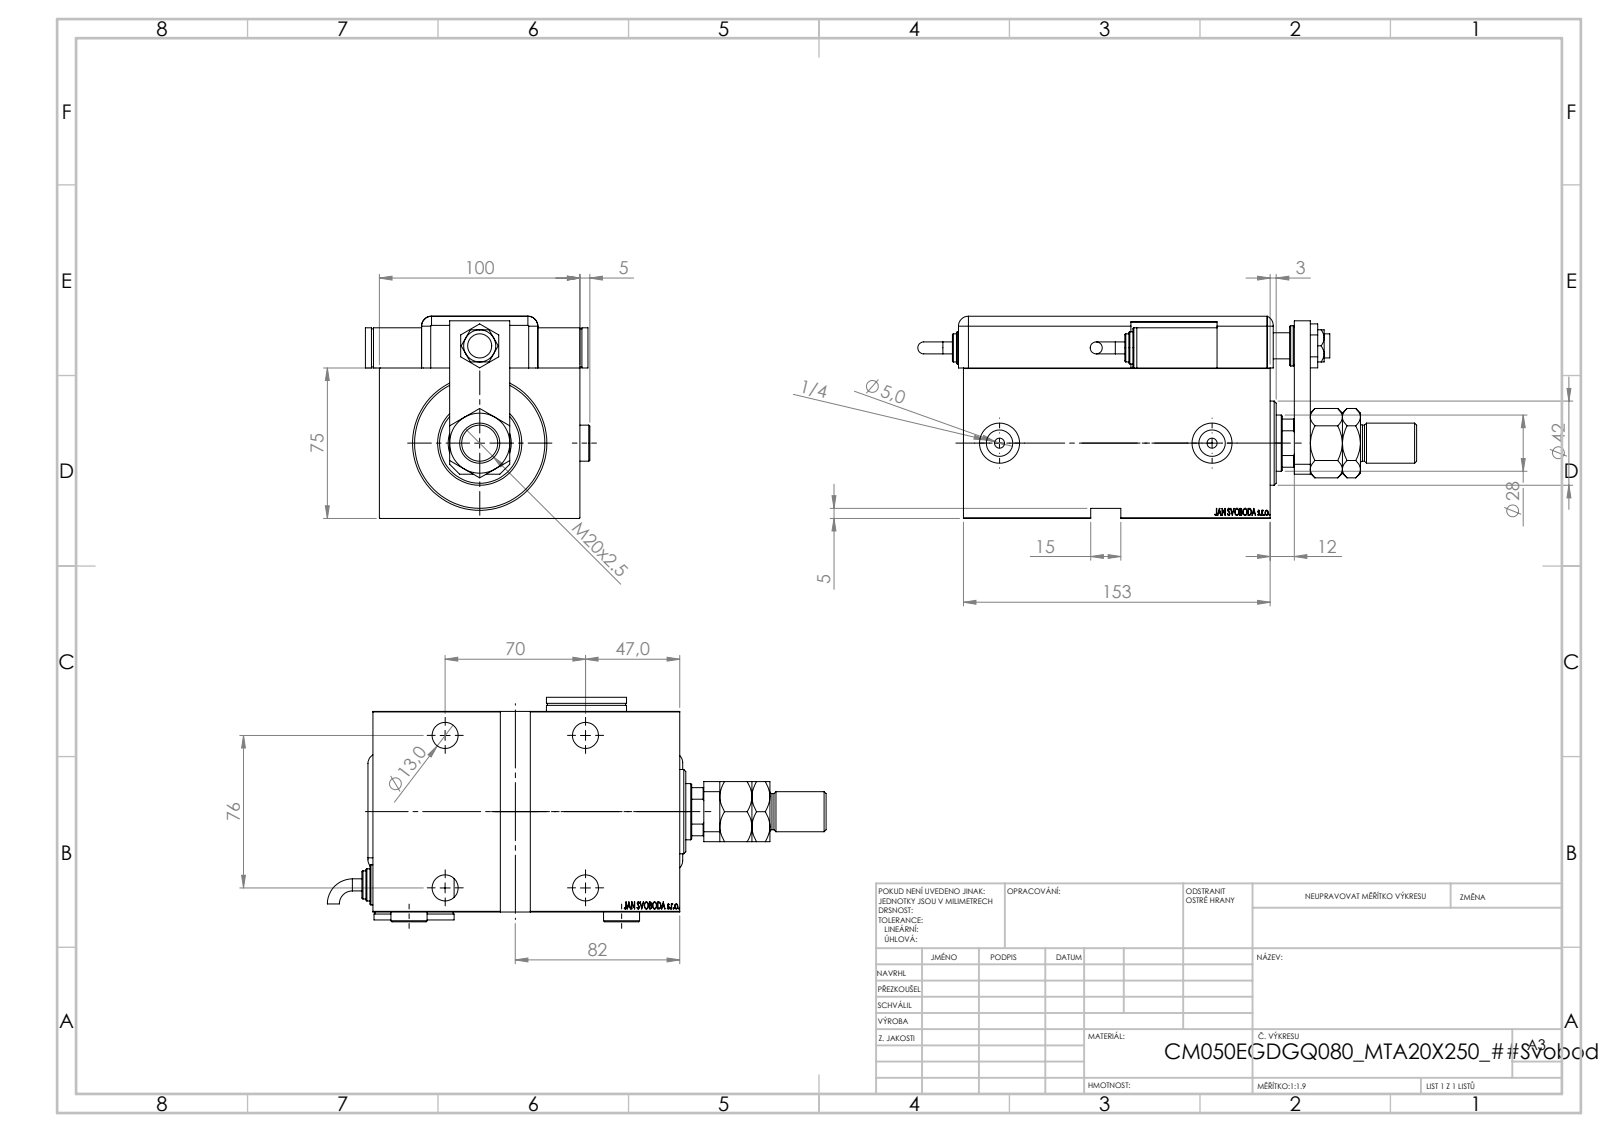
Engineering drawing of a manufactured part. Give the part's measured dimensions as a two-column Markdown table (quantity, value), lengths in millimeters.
| quantity | value |
| --- | --- |
| part name | SWITCH DIM A_G; MAGNETIC SWITCH Q; V450CM_VC_B; TYC (+7 more) |
| STEP written by | SolidWorks 2019 (CONFIG_CONTROL_DESIGN) |
| units | millimeters |
| bodies | 16 solids, 1345 faces (667 planar, 127 cylindrical, 551 other) |
| overall size | 248.76 × 111.9 × 100.8 |
| volume | 1 178 000 mm³ |
| surface area | 214 663 mm² |
| round holes (diameter × count) | 13 × 5, 19 × 4, 20 × 3, 4 × 2, 5 × 2, 8 × 2, 13.16 × 2, 12 × 1, 14 × 1, 18.5 × 1, 28 × 1, 31.5 × 1 |
| round bosses / shafts (diameter × count) | 20 × 3, 18 × 3, 16 × 2, 14 × 2, 6 × 2, 52 × 1, 42 × 1 |
| partial cylindrical surfaces (radius × count) | 5 × 9, 10 × 1, 13.5 × 1 |
| main face-to-face distances | 3, 75, 100, 100.8, 25.8, 14, 153, 20, 22.8, 97.8 |
| hole center spacings | 47.2, 61.22, 70, 76, 103.32, 111.57, 118.19, 20 |
